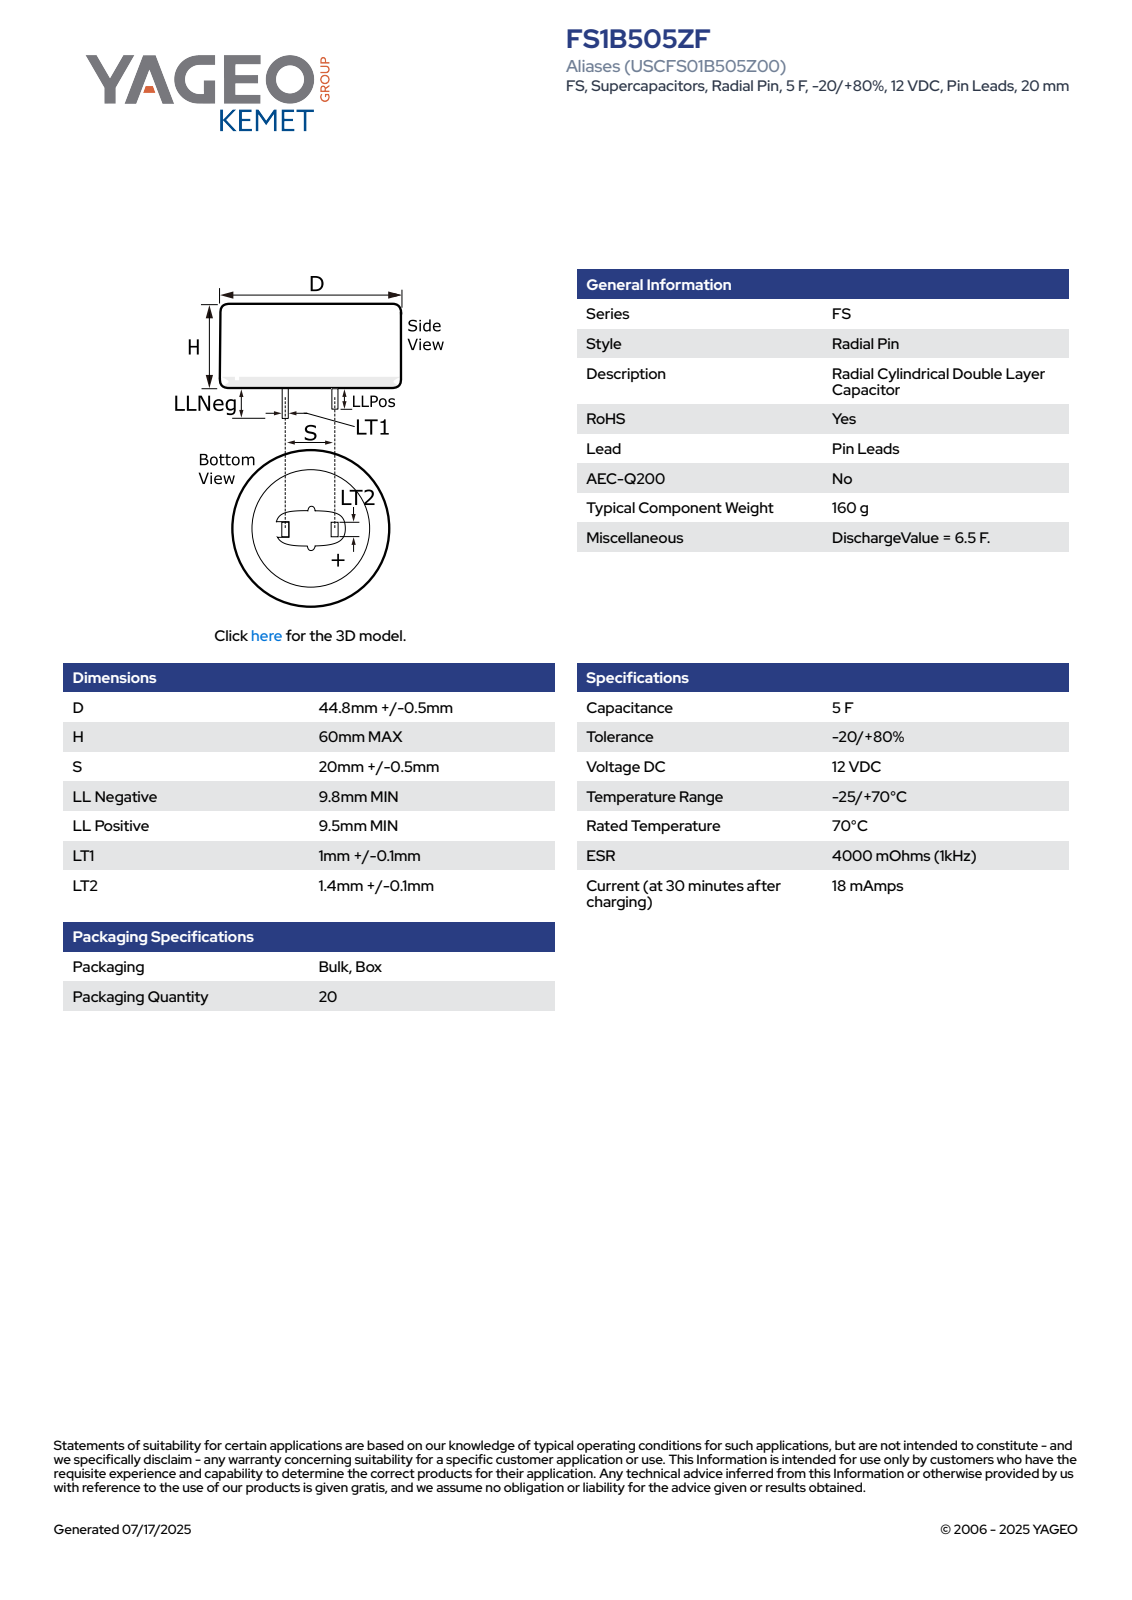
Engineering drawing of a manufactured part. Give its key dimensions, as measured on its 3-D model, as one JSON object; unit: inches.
{"part_name": "CDR_LPLLN_D45.3L60S20LLNEG9.8LLPOS9.5LT11.1LT21.5", "step_written_by": "SolidWorks 2014 (AUTOMOTIVE_DESIGN)", "units": "inches", "bodies": {"solids": 1, "faces": 78, "planar": 70, "cylindrical": 4, "other": 4}, "overall_size": [2.748, 1.783, 1.783], "volume_in3": 5.849, "surface_area_in2": 17.64, "round_bosses_or_shafts": [[1.783, 1]], "partial_cylinders_radius": [[0.892, 1]], "face_to_face_distances": [2.362, 0.043, 0.787, 0.059, 0.831, 0.744, 2.362, 0.386, 2.748, 2.748]}
